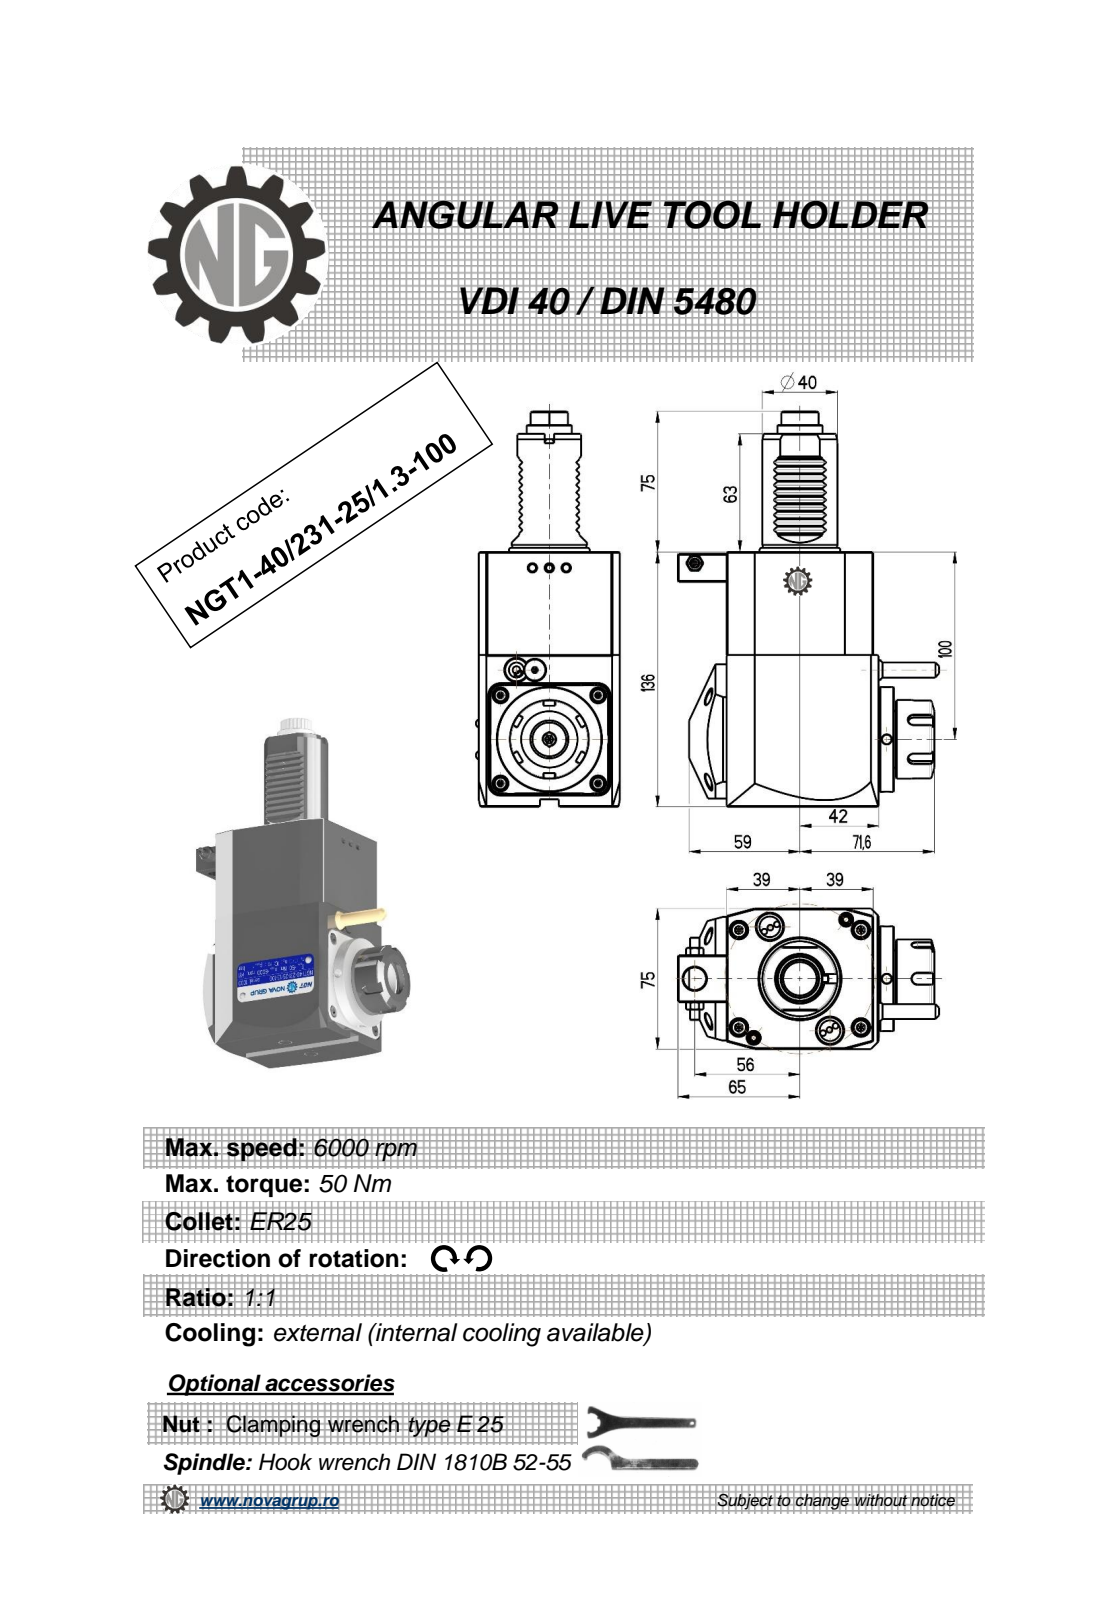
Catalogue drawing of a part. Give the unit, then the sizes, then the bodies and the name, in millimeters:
Units: millimetres
Overall size (bounding box): 211 × 139.14 × 75
Round holes (diameter × count): ⌀5 ×3, ⌀3 ×1, ⌀4.2 ×1, ⌀9.5 ×1, ⌀12 ×1, ⌀20.3 ×1
Round bosses / shafts (diameter × count): ⌀56 ×1, ⌀43 ×1, ⌀42 ×1, ⌀40 ×1, ⌀33 ×1, ⌀24 ×1, ⌀11.2 ×1, ⌀8.96 ×1
Partial cylindrical surfaces — rounded edges, fillets, slot ends (radius × count): R2.08 ×48, R0.3 ×20, R0.26 ×12, R0.22 ×6, R3 ×5, R9.08 ×1, R9.92 ×1, R15 ×1
Main face-to-face distances: 75, 136, 78, 81, 3, 11, 8, 84.88, 8.2, 7.5
Hole centre spacings: 40.93, 57.24, 91.5, 102.25, 138.89
Volume: 979 708 mm³ · Surface area: 76 623 mm²
Bodies: 1 solid, 595 faces (229 planar, 191 cylindrical, 175 other)
Part name (STEP PRODUCT): NGT1_40_231_25_1_3_100
STEP written by: PRO/ENGINEER BY PARAMETRIC TECHNOLOGY CORPORATION, 2010280 (CONFIG_CONTROL_DESIGN)
